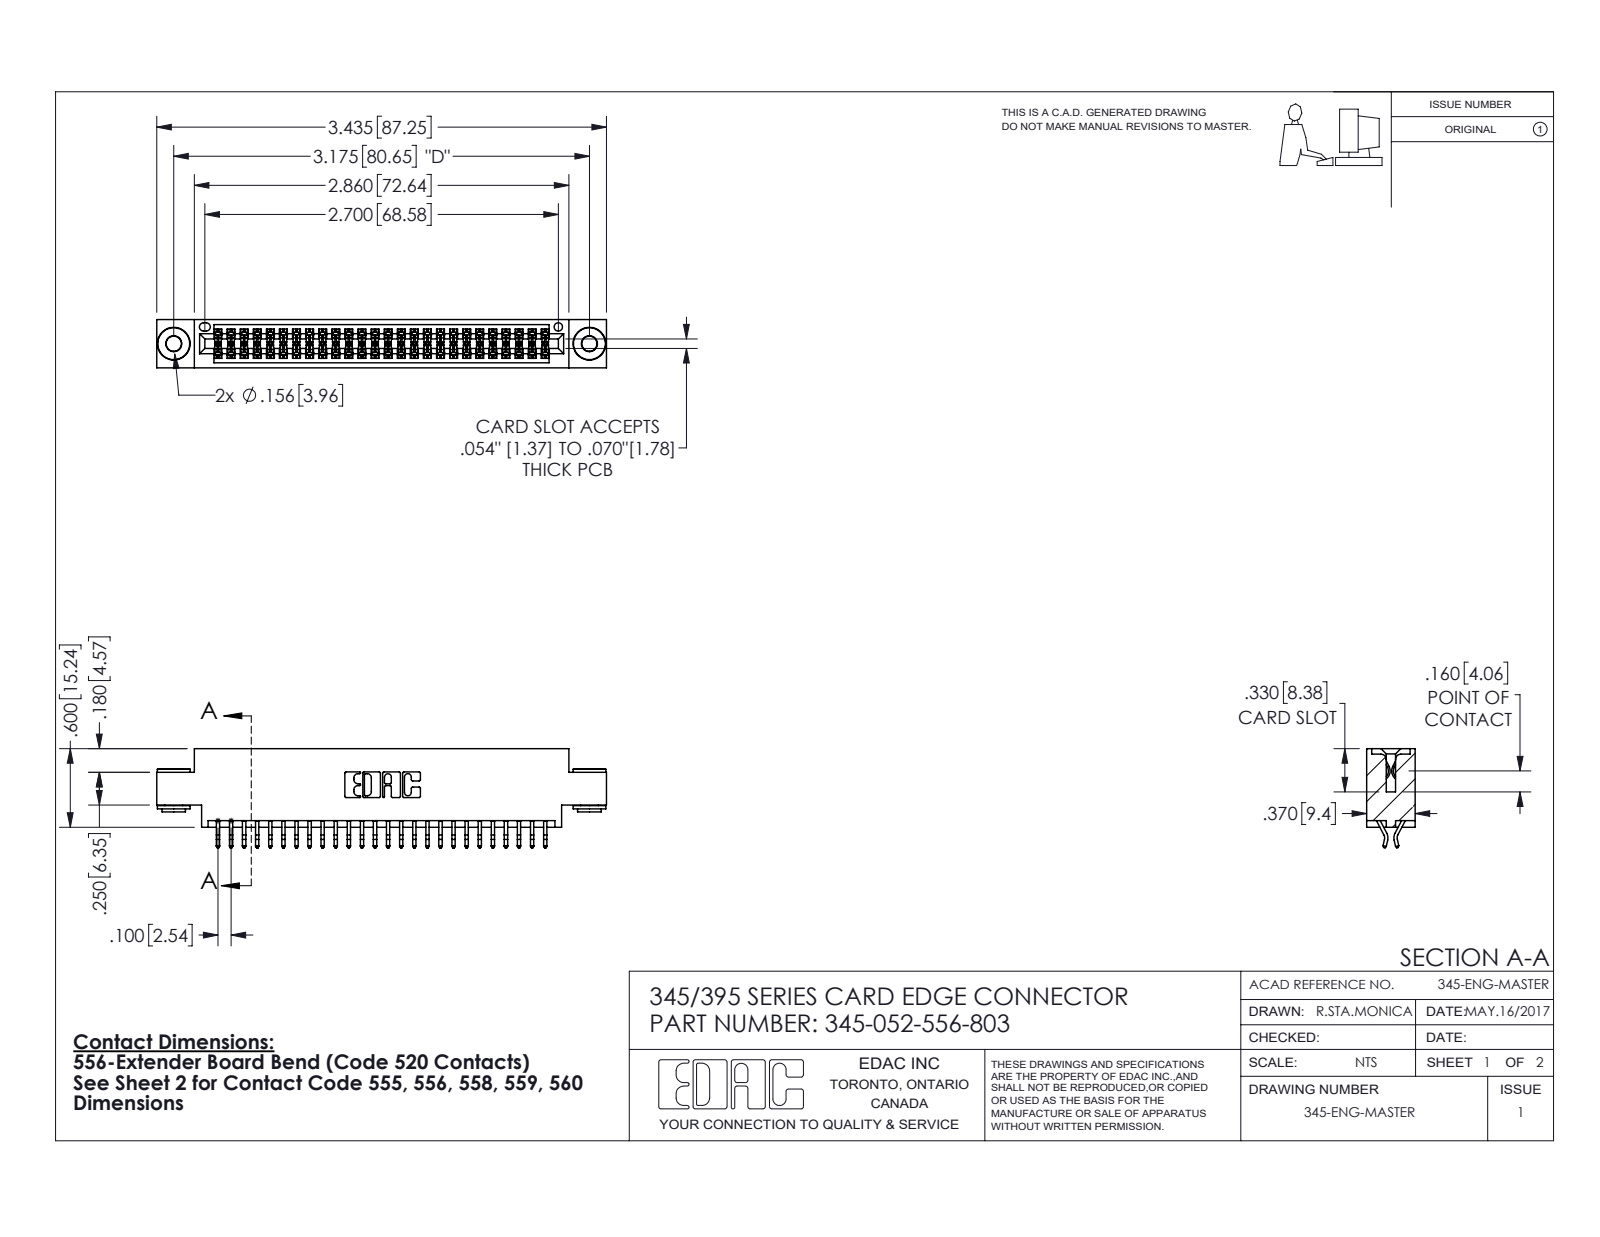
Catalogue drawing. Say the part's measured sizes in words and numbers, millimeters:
The part is named "345-052-556-803; 345-250-002_345-250-002-102; 345 Part_0.170 Offset - 0.156 Dia-TH; 345-292-001_556 Tail". Its 3-D file was written by "SolidWorks 2016 (CONFIG_CONTROL_DESIGN)". It is 55 solids with 3080 faces: 2018 planar, 1054 cylindrical and 8 other. Overall it measures 87.2 by 19.2 by 9.4 millimeters. Its volume is 8 230 cubic millimeters and its surface area 12 160 square millimeters. Round holes: 2 of diameter 2.9, 2 of diameter 4, 1 of diameter 1.6. Round bosses or shafts: 2 of diameter 6.4, 2 of diameter 4.6, 2 of diameter 3.5. Partial cylindrical surfaces (rounded edges, fillets, slot ends): 78 of radius 0.2, 22 of radius 0.3, 6 of radius 0.2, 6 of radius 0.8, 3 of radius 0.7, 2 of radius 0.3, 2 of radius 0.4, 2 of radius 0.5. The main face-to-face distances are 1.8, 7.6, 9.4, 5.1, 0.6, 2.5, 6.9, 5.7, 4.4, 3.8. The hole center spacings are 6.9, 74.7, 80.6.
